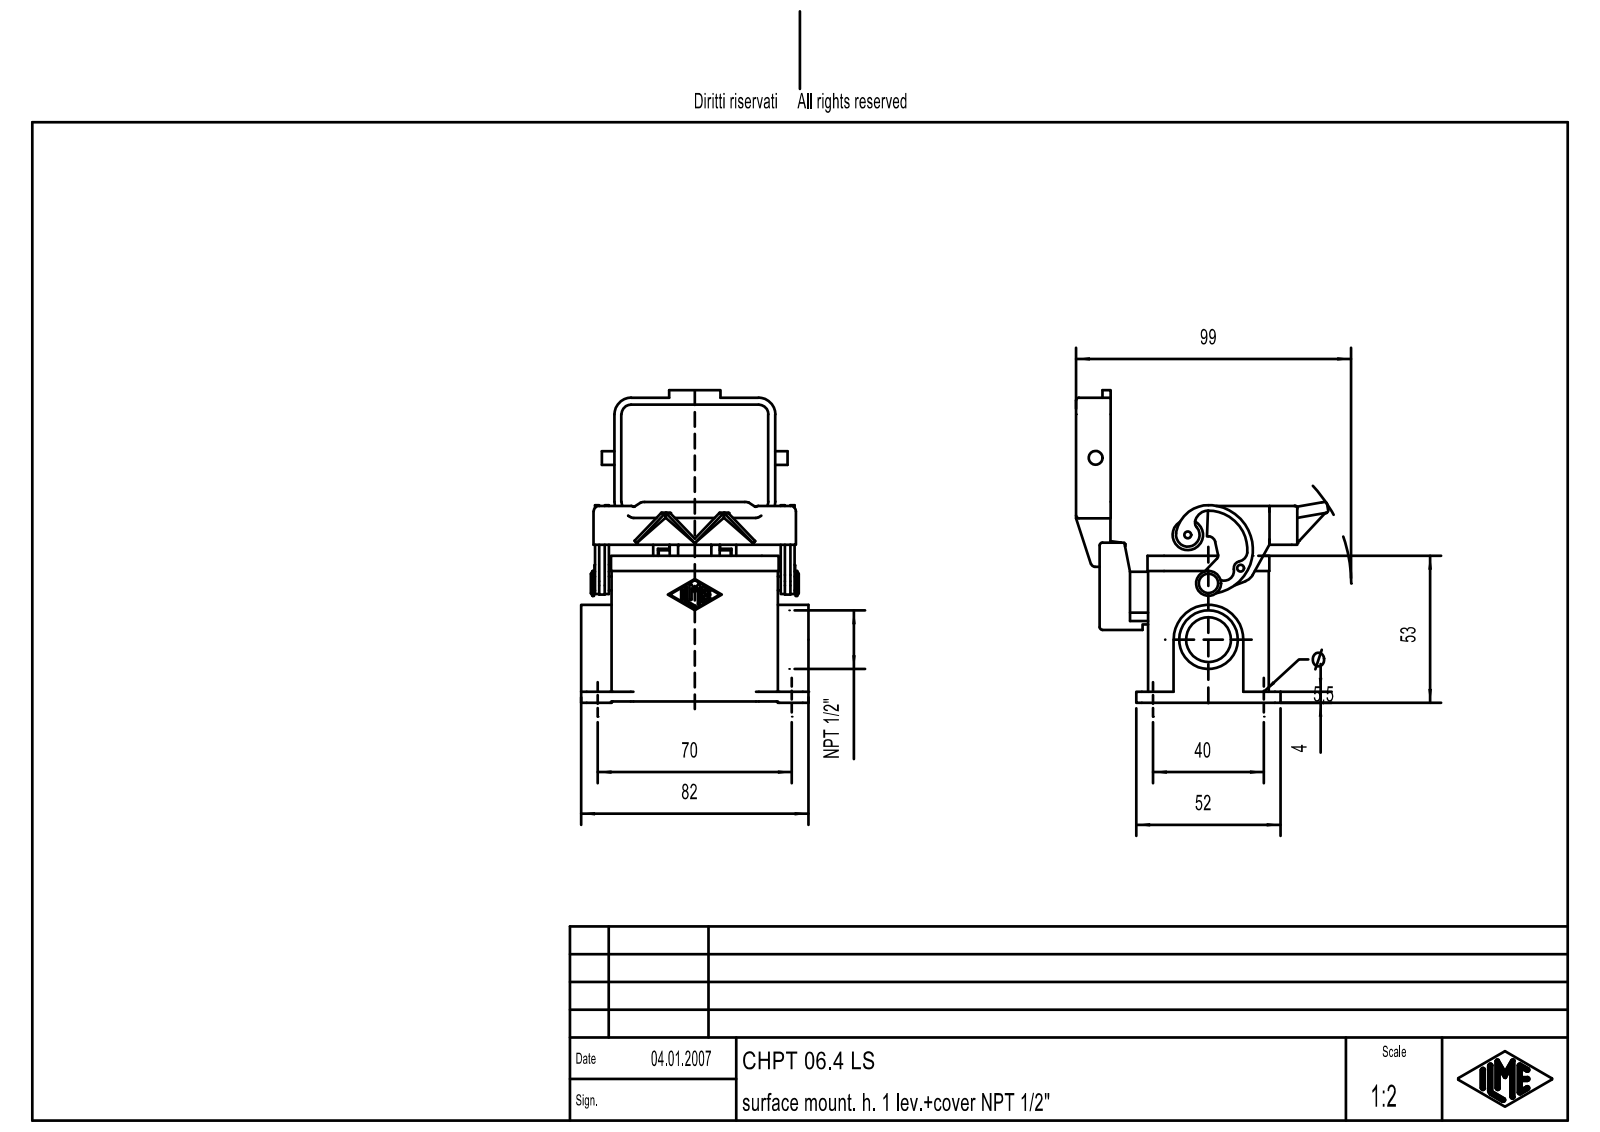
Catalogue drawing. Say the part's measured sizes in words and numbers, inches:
The part is named "MSBO11885.0; MSBO11885.1; MSBO11885". Its 3-D file was written by "Creo Elements/Direct Modeling 18.0B 02-Dec-2011 (C) Parametric Technology GmbH (AUTOMOTIVE_DESIGN)". It is 2 solids with 616 faces: 305 planar, 237 cylindrical and 74 other. Overall it measures 4.437 by 3.581 by 3.228 inches. Its volume is 5.801 cubic inches and its surface area 83.52 square inches. Round holes: 4 of diameter 0.097, 4 of diameter 0.122, 4 of diameter 0.217, 1 of diameter 0.098, 1 of diameter 0.157, 1 of diameter 0.197, 1 of diameter 0.72. Round bosses or shafts: 2 of diameter 0.197, 1 of diameter 0.433, 1 of diameter 0.354, 1 of diameter 0.276, 1 of diameter 0.157, 1 of diameter 0.118, 1 of diameter 0.079. Partial cylindrical surfaces (rounded edges, fillets, slot ends): 28 of radius 0.079, 22 of radius 0.039, 14 of radius 0.015, 12 of radius 0.236, 8 of radius 0.028, 6 of radius 0.059, 6 of radius 0.138, 4 of radius 0.118. The main face-to-face distances are 0.118, 0.138, 1.594, 0.157, 1.713, 2.126, 0.177, 1.024, 1.142, 2.618. The hole center spacings are 0.572, 1.415, 2.259, 2.603, 1.063, 1.575, 1.732, 2.032.
